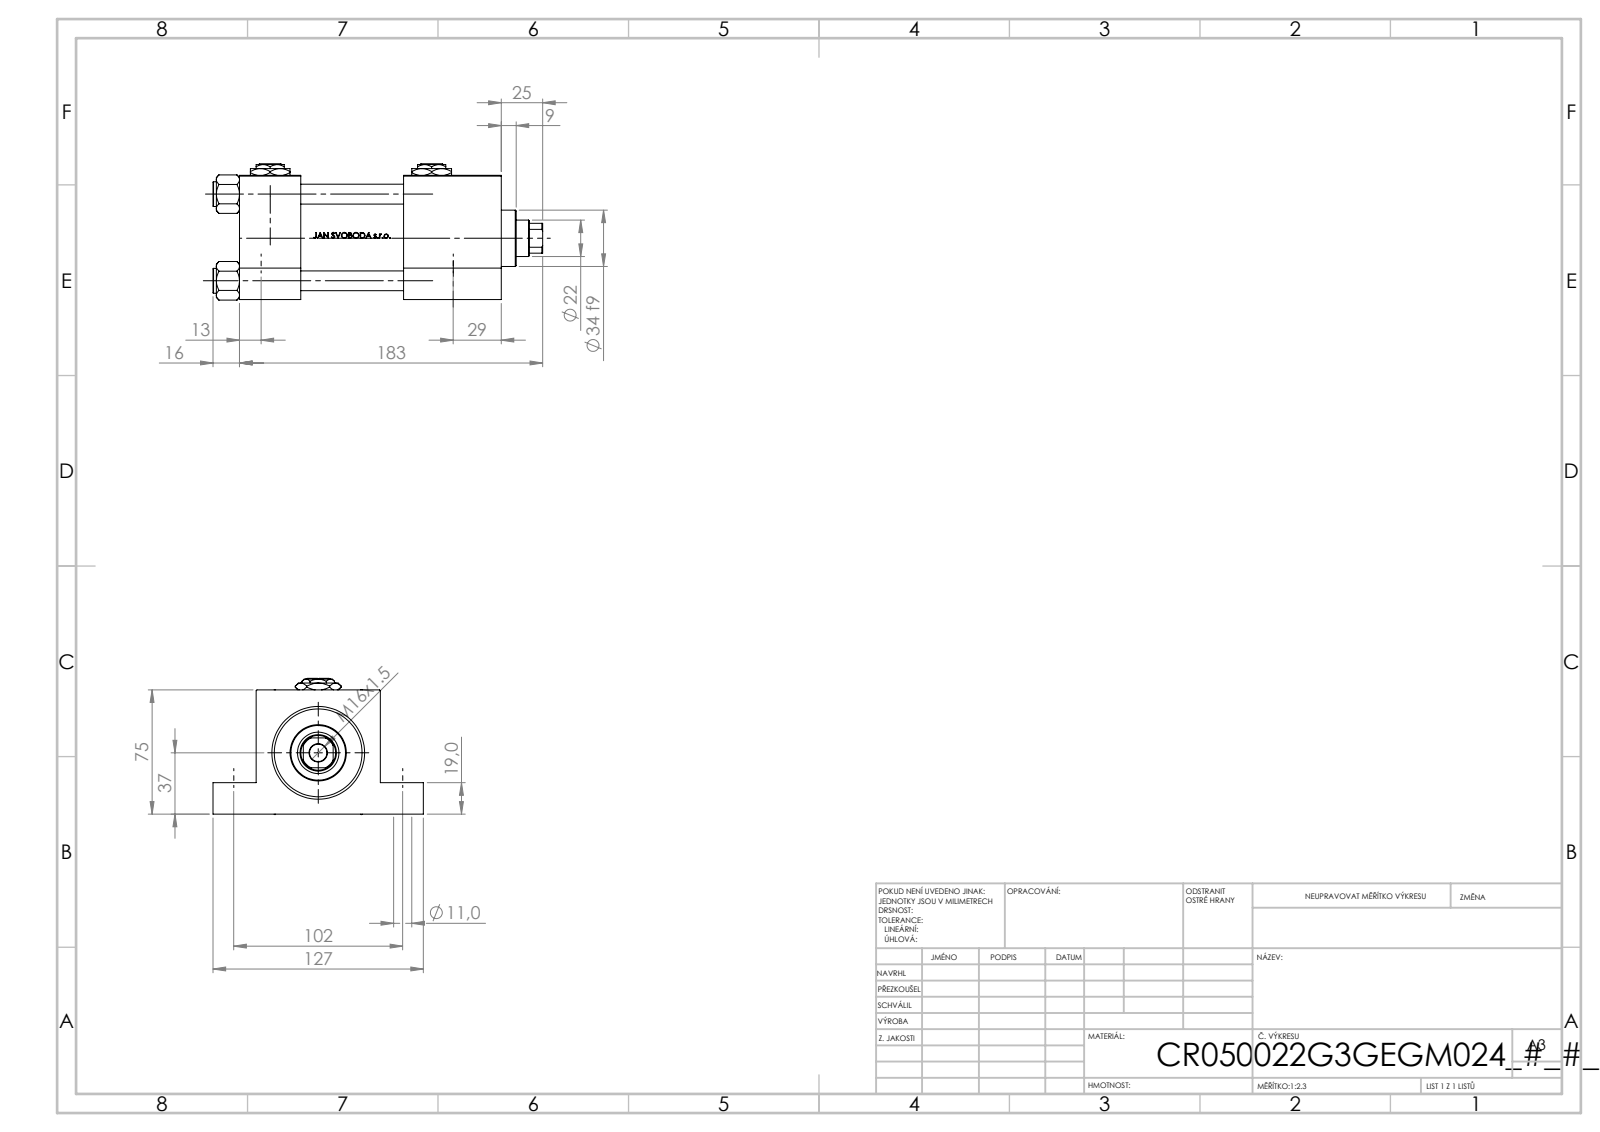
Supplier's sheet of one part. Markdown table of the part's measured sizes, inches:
| quantity | value |
| --- | --- |
| part name | V215CR_G_TYCINKA; V215CR_G_Body; Zatka_pro_OIL_PORT; V215CR_VCP_G (+2 more) |
| STEP written by | SolidWorks 2019 (CONFIG_CONTROL_DESIGN) |
| units | inches |
| bodies | 17 solids, 1252 faces (496 planar, 136 cylindrical, 620 other) |
| overall size | 7.835 × 5 × 3.239 |
| volume | 48.7 in³ |
| surface area | 277.3 in² |
| round holes (diameter × count) | 0.472 × 4, 0.551 × 4, 0.276 × 2, 0.825 × 2, 1.181 × 2, 0.413 × 1, 0.866 × 1, 0.984 × 1, 1.614 × 1, 1.969 × 1, 2.087 × 1 |
| round bosses / shafts (diameter × count) | 0.591 × 4, 2.205 × 1, 1.339 × 1 |
| partial cylindrical surfaces (radius × count) | 0.413 × 1 |
| main face-to-face distances | 2.953, 1.457, 6.22, 4.764, 0.748, 3.898, 2.205, 2.441, 2.323, 1.024 |
| hole center spacings | 1.456, 2.059, 2.02, 2.072, 2.912, 4.016, 4.525, 4.567 |
